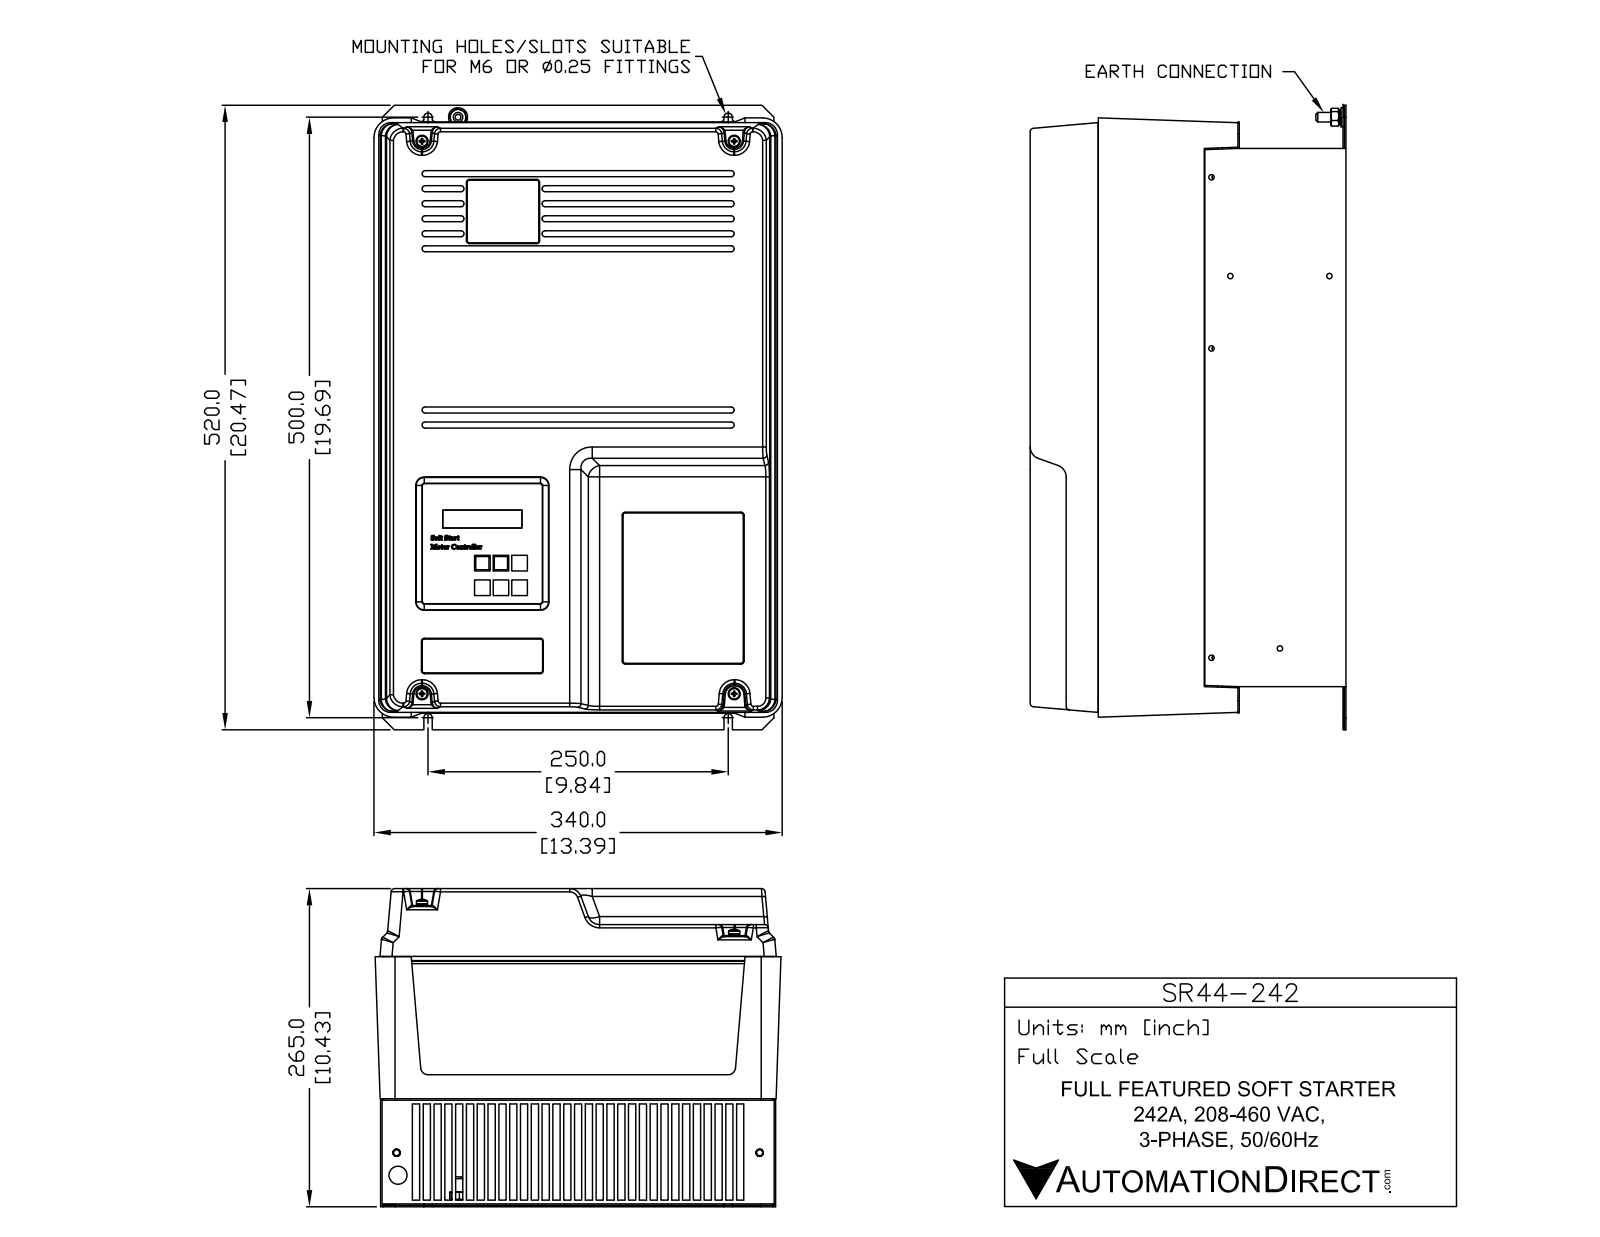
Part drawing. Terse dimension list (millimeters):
name: SR44-242
written by: SolidWorks 2013 (AUTOMOTIVE_DESIGN)
unit: mm
bodies: 1 solid, 828 faces (518 planar, 144 cylindrical, 166 other)
size: 520 × 337.91 × 263
volume: 38 650 000 mm³; area: 1 324 000 mm²
holes: 2× ⌀13
bosses: 4× ⌀10, 1× ⌀16, 1× ⌀8
rounds: 31× R5, 16× R3, 12× R2.4, 8× R1.5, 8× R15, 6× R2, 4× R3.5, 2× R10
face distances: 8.9, 17.8, 26.7, 35.6, 263, 5.75, 14.65, 44.5, 3.15, 23.55
hole spacings: 250
